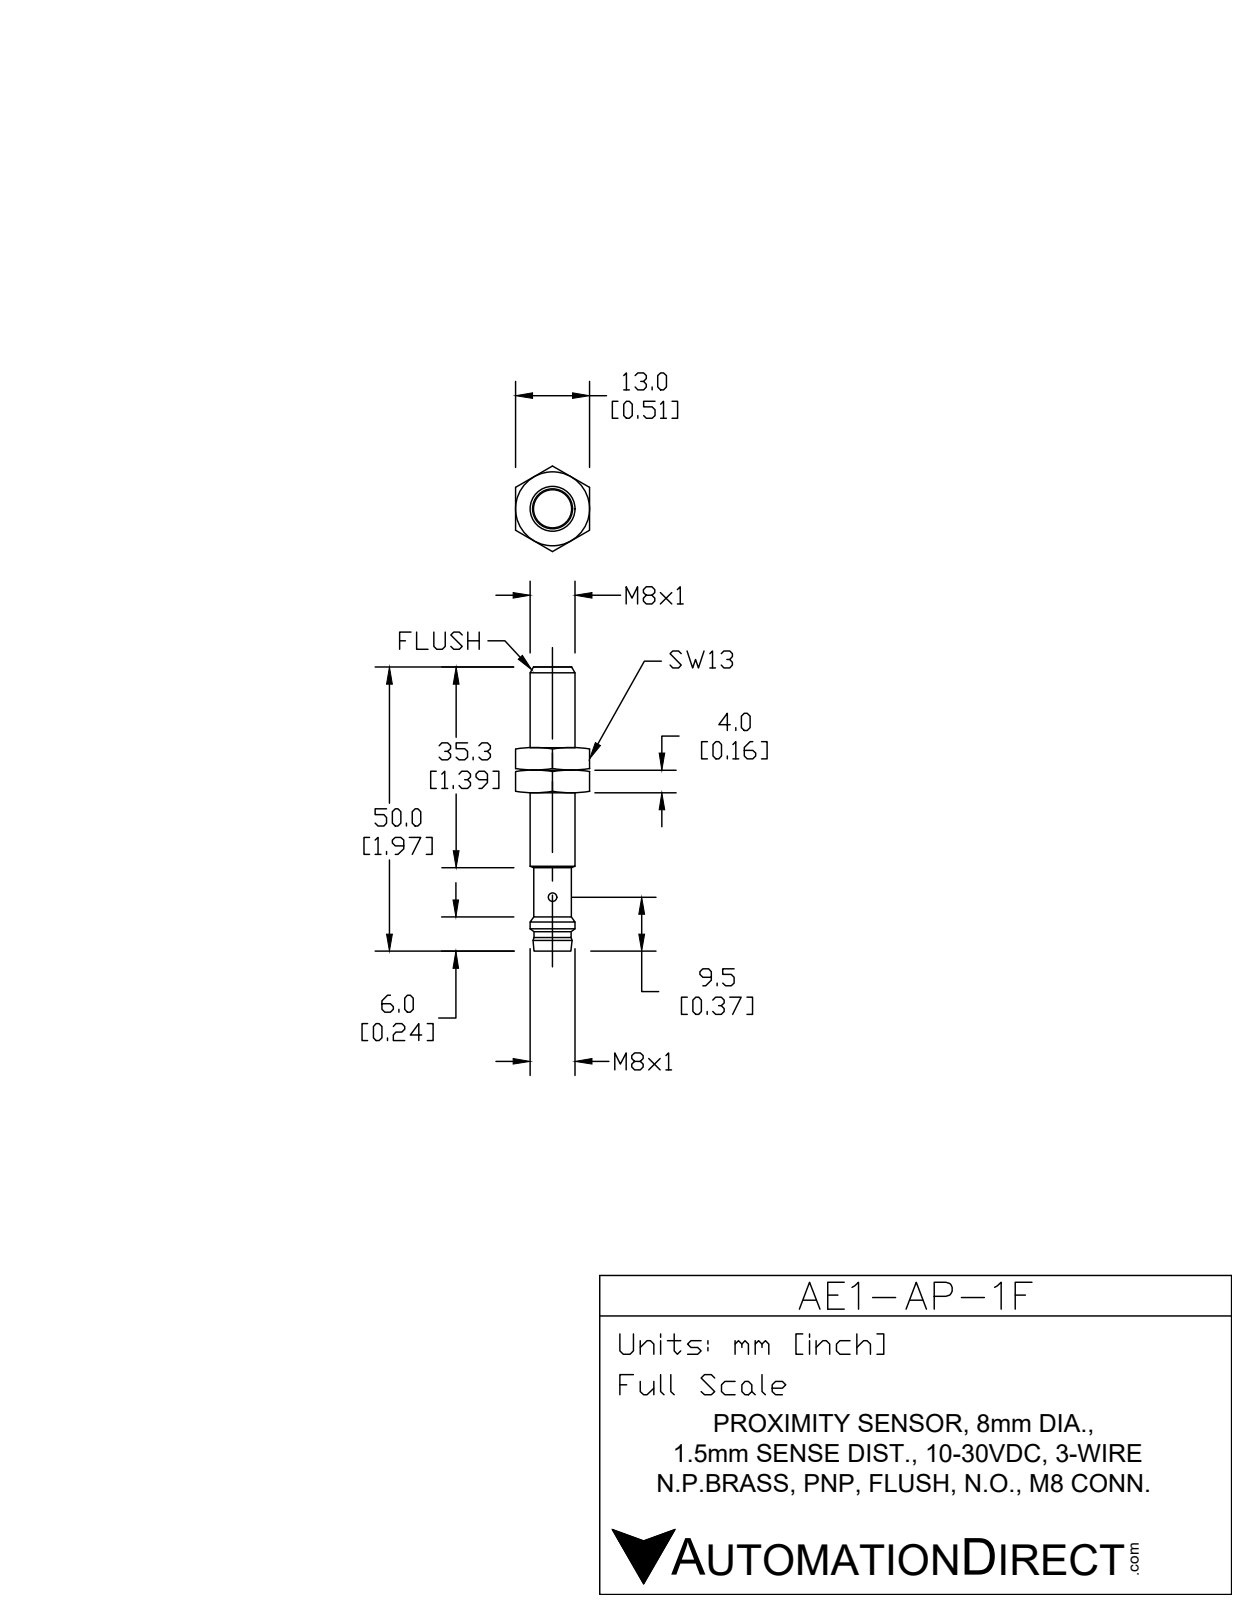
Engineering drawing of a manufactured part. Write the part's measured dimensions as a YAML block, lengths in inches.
part_name: "AE1-AP-1F"
step_written_by: "SolidWorks 2017 (AUTOMOTIVE_DESIGN)"
units: inches
bodies: {solids: 3, faces: 61, planar: 11, cylindrical: 30, other: 20}
overall_size: [1.969, 0.315, 0.315]
volume: 0.143
surface_area: 2.594
round_holes:
  - {diameter: 0.079, count: 2}
  - {diameter: 0.23, count: 1}
round_bosses_or_shafts:
  - {diameter: 0.039, count: 3}
  - {diameter: 0.315, count: 1}
  - {diameter: 0.272, count: 1}
  - {diameter: 0.256, count: 1}
face_to_face_distances: [1.772, 1.783, 1.516, 1.504, 0.268, 1.76, 0.256, 1.969, 1.957, 0.453]
